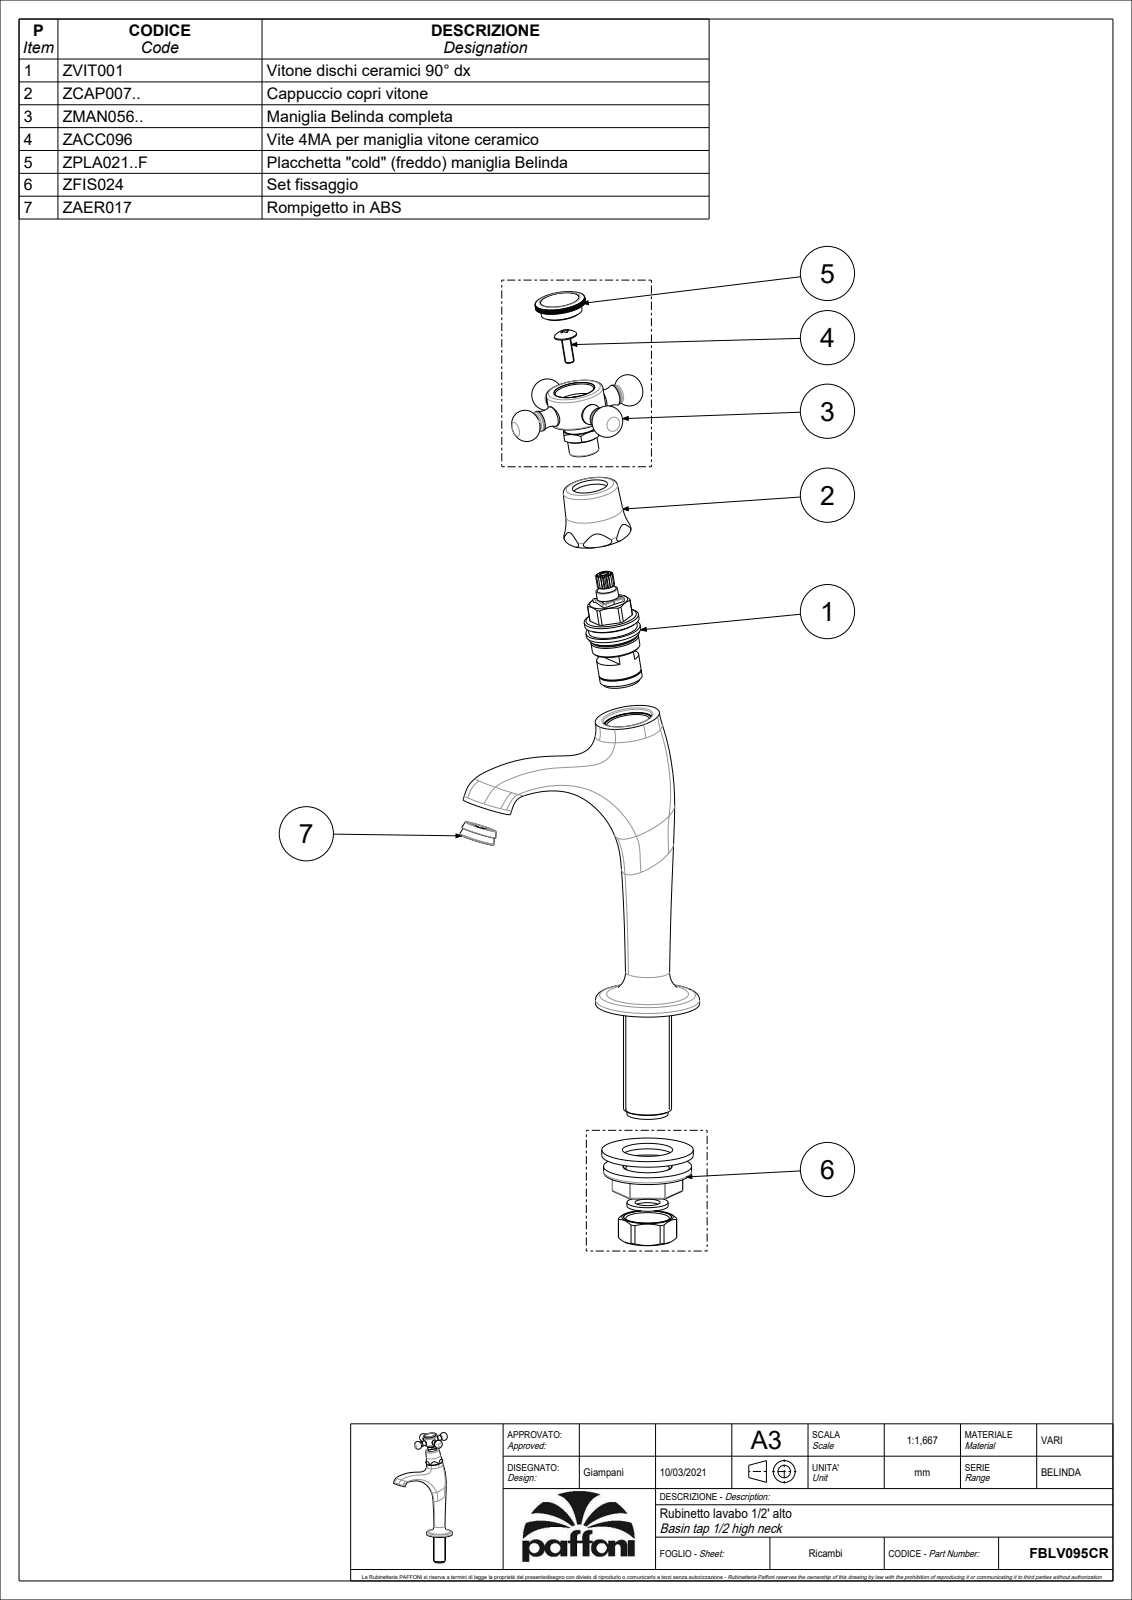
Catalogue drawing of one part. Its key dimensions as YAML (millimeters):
part_name: "FBLV095CR"
step_written_by: "CREO PARAMETRIC BY PTC INC, 2020044 (CONFIG_CONTROL_DESIGN)"
units: millimeters
bodies: {solids: 1, faces: 470, planar: 225, cylindrical: 136, other: 109}
overall_size: [183.57, 114.12, 64.07]
volume: 122788
surface_area: 25080
round_bosses_or_shafts:
  - {diameter: 9, count: 3}
  - {diameter: 7, count: 3}
  - {diameter: 45.5, count: 1}
  - {diameter: 25, count: 1}
  - {diameter: 21.7, count: 1}
  - {diameter: 14, count: 1}
  - {diameter: 13, count: 1}
partial_cylinders:
  - {radius: 11, count: 1}
face_to_face_distances: [11.4, 23.81, 35.21, 26.8, 15, 26.79, 15.2, 4, 27.21, 3.4]
